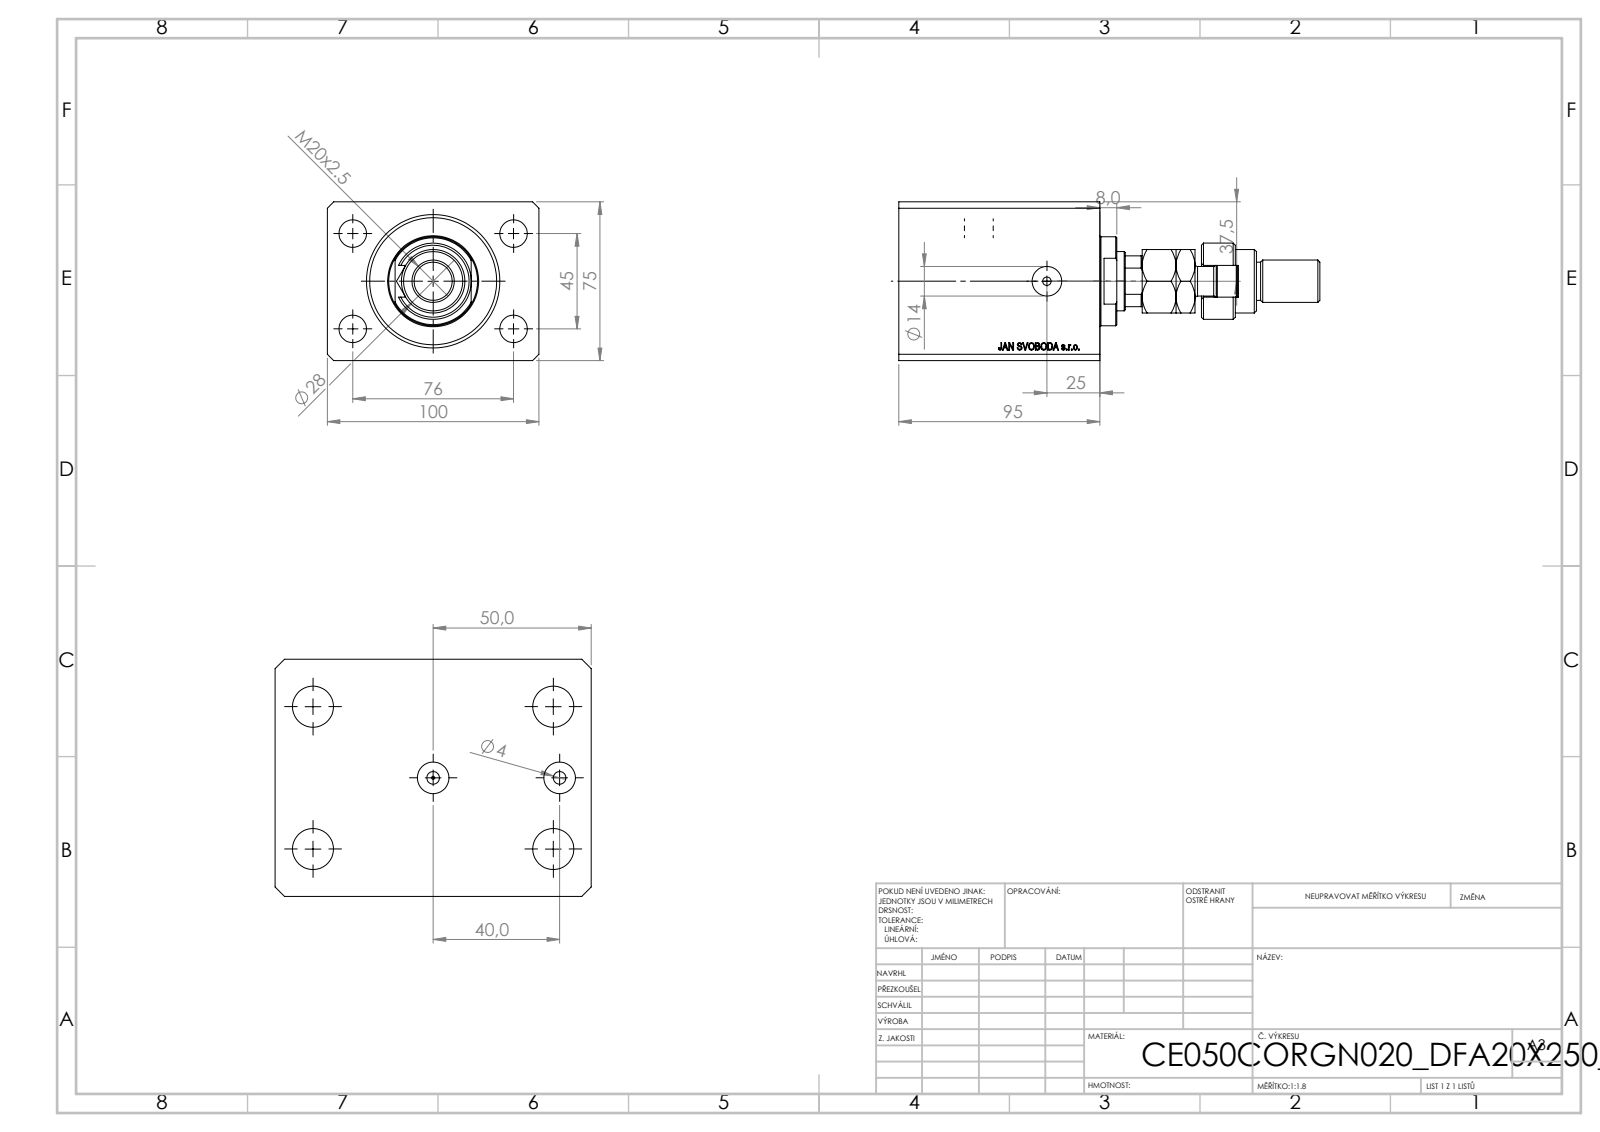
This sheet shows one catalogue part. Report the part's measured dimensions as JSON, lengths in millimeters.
{"part_name": "V250CE_C_VCP; FEMALE_PART_FOR_DFA; MFA; V250CE_VC_C (+1 more)", "step_written_by": "SolidWorks 2019 (CONFIG_CONTROL_DESIGN)", "units": "millimeters", "bodies": {"solids": 5, "faces": 953, "planar": 456, "cylindrical": 59, "other": 438}, "overall_size": [198.9, 100, 75], "volume_mm3": 686240, "surface_area_mm2": 123589, "round_holes": [[4, 4], [13, 4], [10, 2], [14, 2], [1.25, 1], [18.5, 1], [28, 1], [50, 1], [63, 1]], "round_bosses_or_shafts": [[42, 1], [36, 1], [30, 1], [22, 1], [20, 1], [18, 1], [14, 1]], "partial_cylinders_radius": [[7.5, 1], [12, 1], [13.5, 1]], "face_to_face_distances": [75, 100, 95, 11.9, 83.1, 68.4, 56.5, 26.6, 30, 20], "hole_center_spacings": [44.16, 45, 22.59, 76, 81.18, 88.32, 40]}
